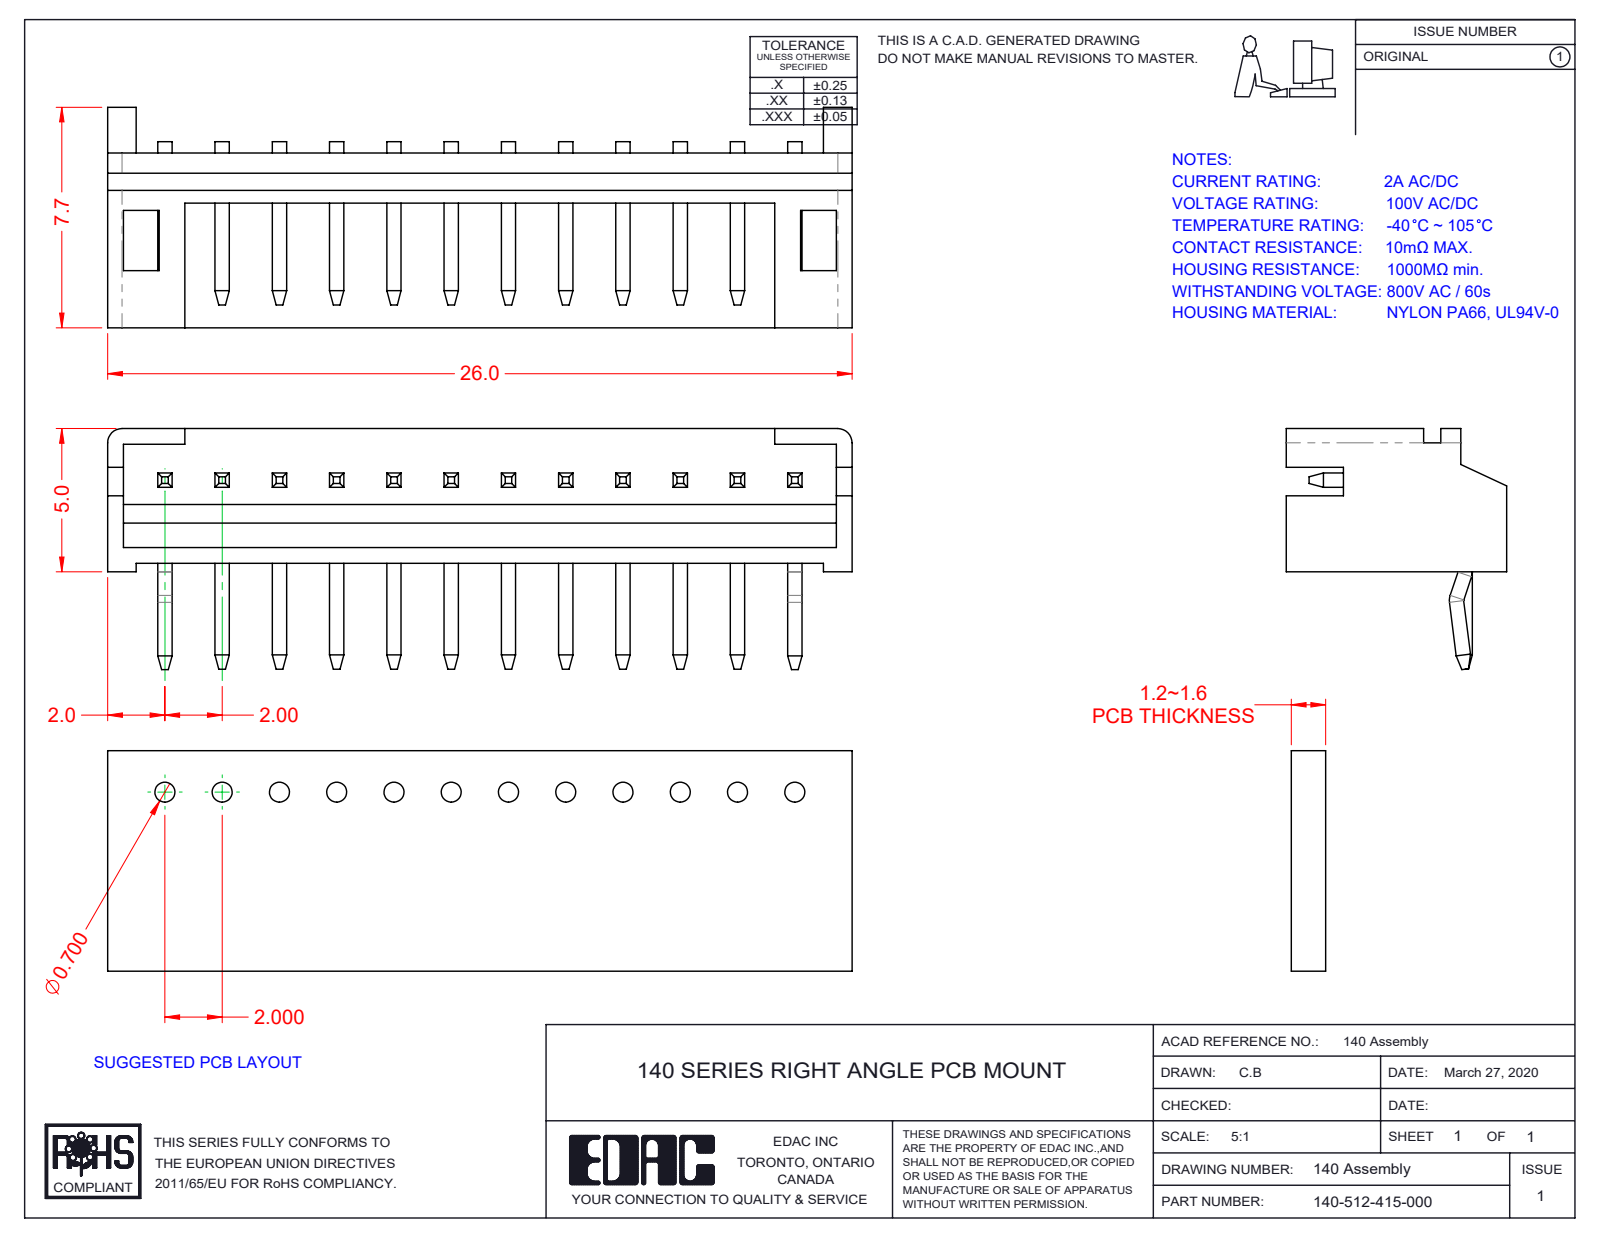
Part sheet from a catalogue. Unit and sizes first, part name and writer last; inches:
Units: inches
Overall size (bounding box): 1.024 × 0.331 × 0.303
Partial cylindrical surfaces — rounded edges, fillets, slot ends (radius × count): R0.02 ×2, R0.022 ×2, R0.006 ×1, R0.026 ×1
Main face-to-face distances: 0.022, 0.059, 0.02, 0.236, 0.079, 0.157, 0.069, 0.163, 0.039, 0.026
Volume: 0.018 in³ · Surface area: 1.711 in²
Bodies: 13 solids, 439 faces (403 planar, 36 cylindrical, 0 other)
Part name (STEP PRODUCT): 140-512-415-000; RA Contact_Str; RA Contact_Kink; RA Housing_512
STEP written by: SolidWorks 2016 (CONFIG_CONTROL_DESIGN)
